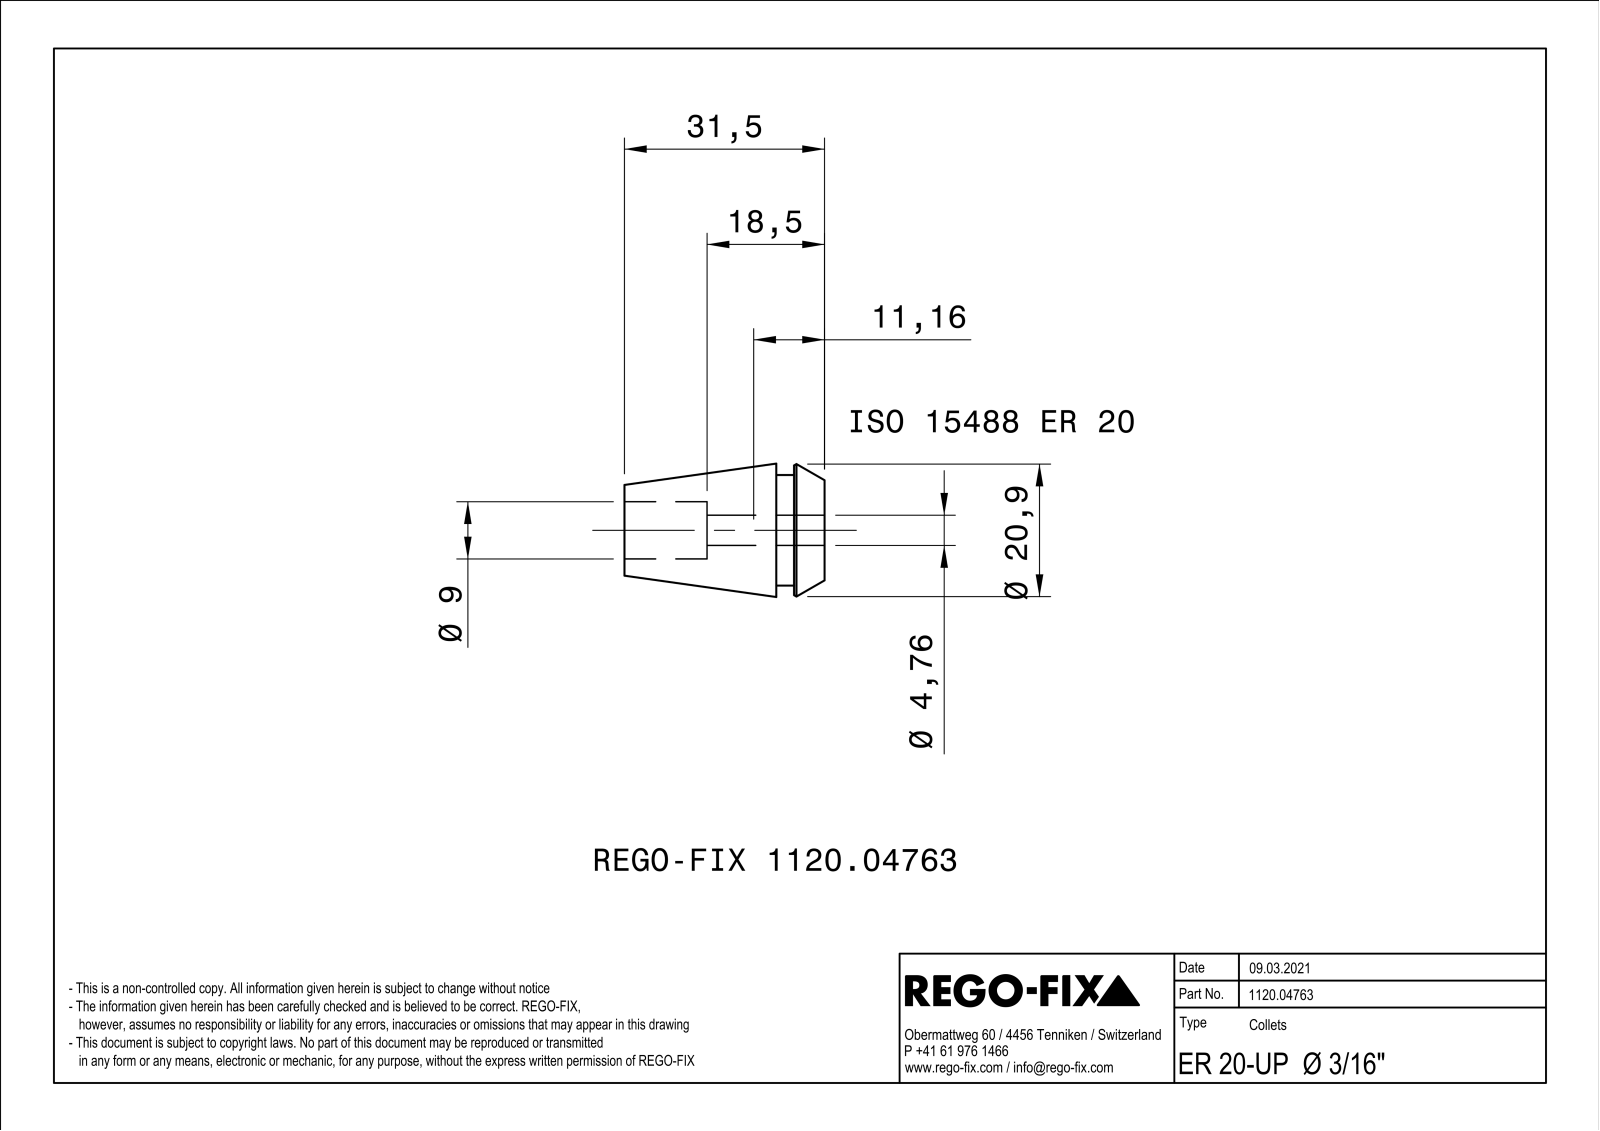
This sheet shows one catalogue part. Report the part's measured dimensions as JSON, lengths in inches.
{"part_name": "NOCUT", "step_written_by": "SIEMENS PLM Software Solid Edge ST10 (AUTOMOTIVE_DESIGN)", "units": "inches", "bodies": {"solids": 1, "faces": 257, "planar": 104, "cylindrical": 41, "other": 112}, "overall_size": [1.24, 0.826, 0.826], "volume_in3": 0.335, "surface_area_in2": 10.17, "round_holes": [[0.354, 1]], "round_bosses_or_shafts": [[0.685, 1]], "partial_cylinders_radius": [[1.575, 8], [0.094, 1]], "face_to_face_distances": [0.024, 0.023, 0.024, 0.299, 0.189, 0.11, 1.24, 1.051, 0.941, 0.728]}
